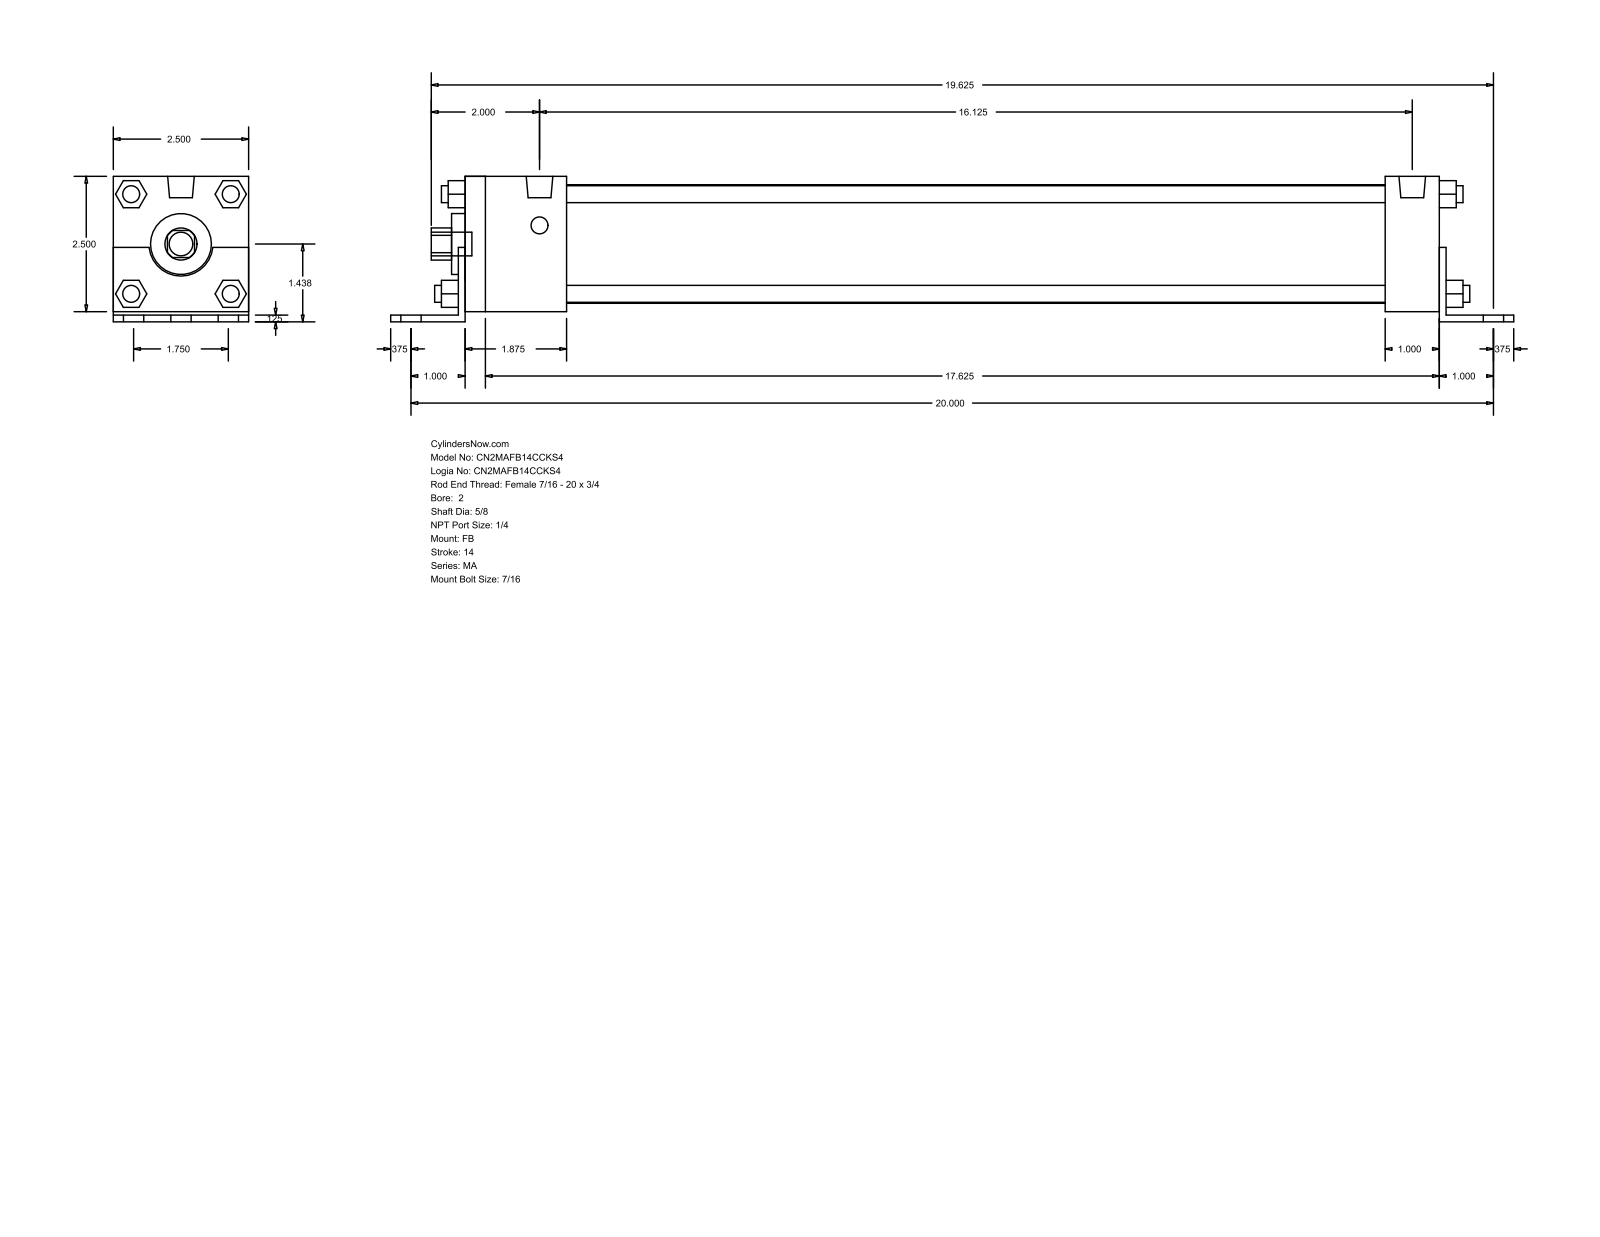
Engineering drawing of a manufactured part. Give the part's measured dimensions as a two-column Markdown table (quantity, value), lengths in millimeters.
| quantity | value |
| --- | --- |
| part name | MA_FB__0200_0.625 |
| STEP written by | GSSL Pune (CONFIG_CONTROL_DESIGN) |
| units | millimeters |
| bodies | 0 solids, 140 faces (105 planar, 35 cylindrical, 0 other) |
| overall size | 527.05 × 68.26 × 63.5 |
| round holes (diameter × count) | 15.88 × 1, 28.57 × 1, 55.63 × 1 |
| round bosses / shafts (diameter × count) | 7.94 × 8, 11.11 × 7, 12.49 × 2 |
| partial cylindrical surfaces (radius × count) | 7.54 × 1, 15.05 × 1 |
| main face-to-face distances | 63.5, 4.76, 3.17, 68.26, 1.59, 3.18, 65.09, 460.37, 457.19, 12.7 |
